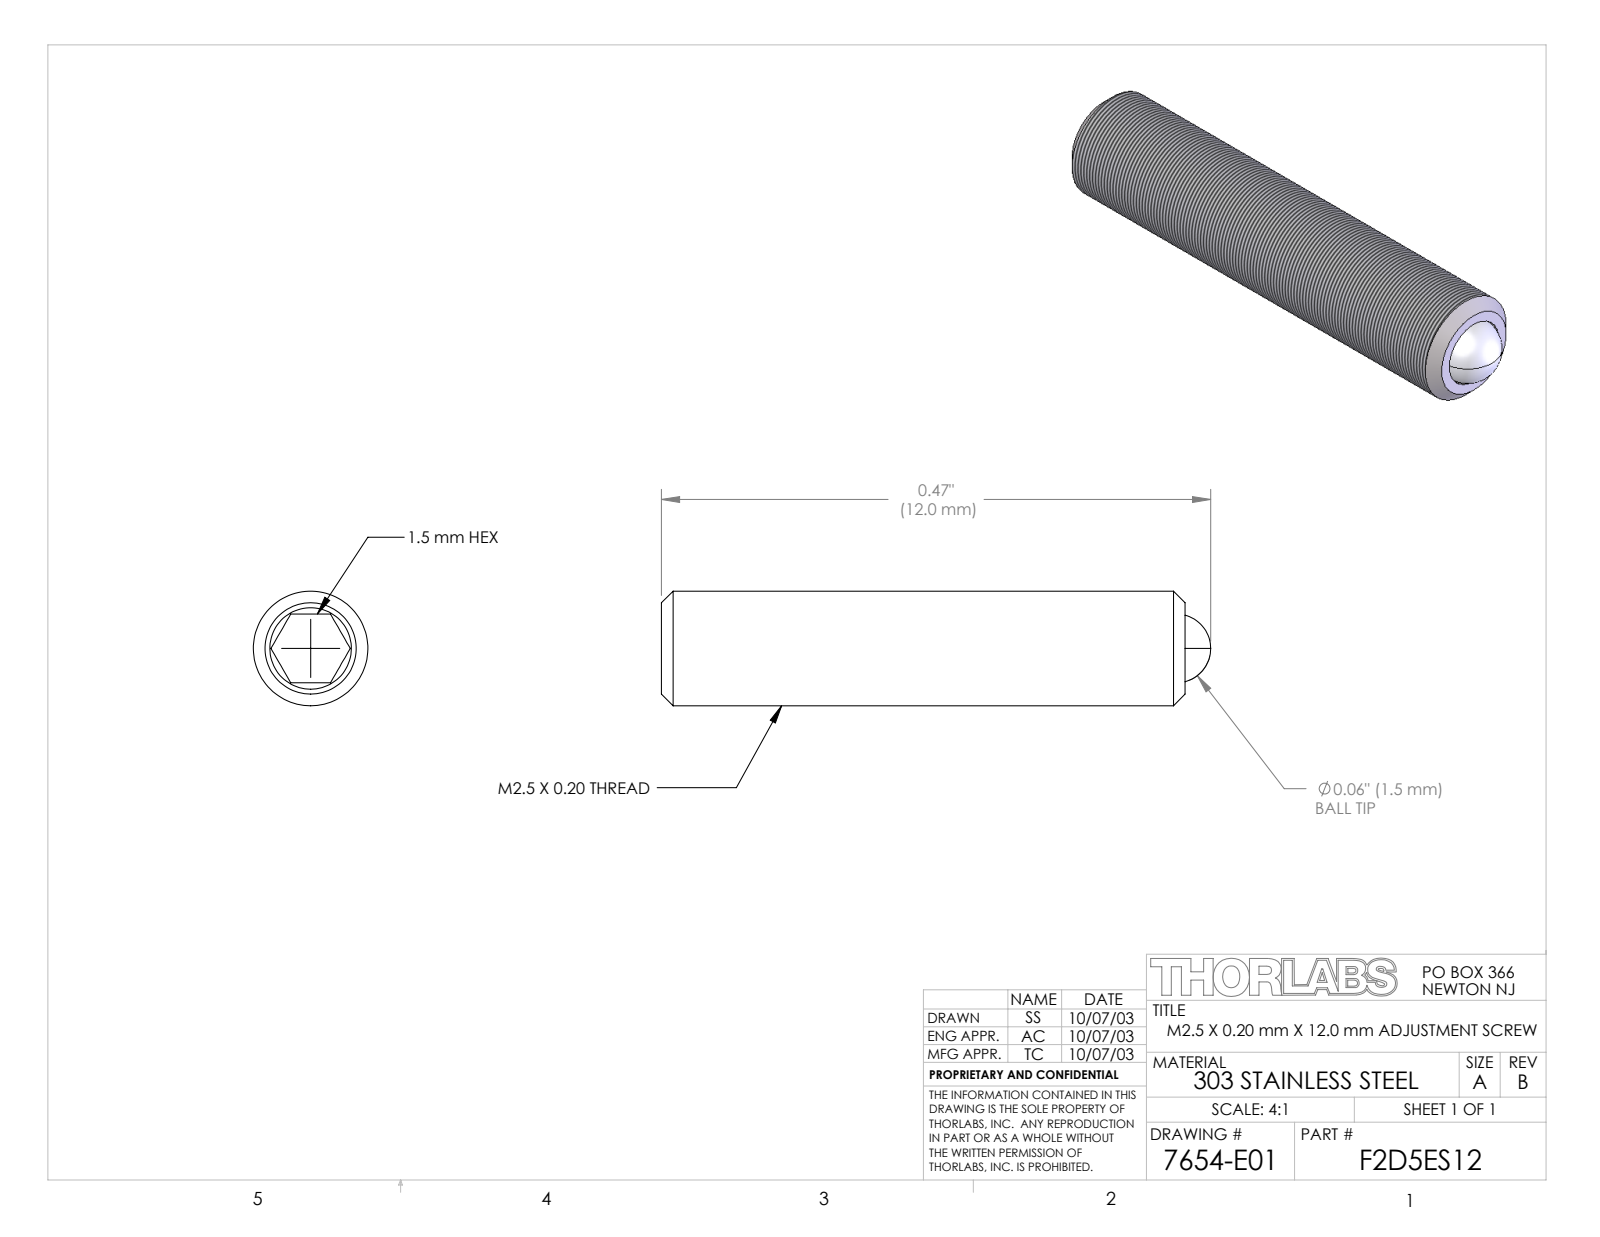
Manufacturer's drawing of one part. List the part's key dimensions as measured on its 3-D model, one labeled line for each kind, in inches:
Part name (STEP PRODUCT): 7654-E0W
STEP written by: SolidWorks 2011 (AUTOMOTIVE_DESIGN)
Units: inches
Bodies: 2 solids, 25 faces (9 planar, 4 cylindrical, 12 other)
Overall size (bounding box): 0.494 × 0.098 × 0.098
Volume: 0.003 in³ · Surface area: 0.197 in²
Round holes (diameter × count): ⌀0.059 ×1
Round bosses / shafts (diameter × count): ⌀0.098 ×1
Main face-to-face distances: 0.059, 0.352, 0.472, 0.12
